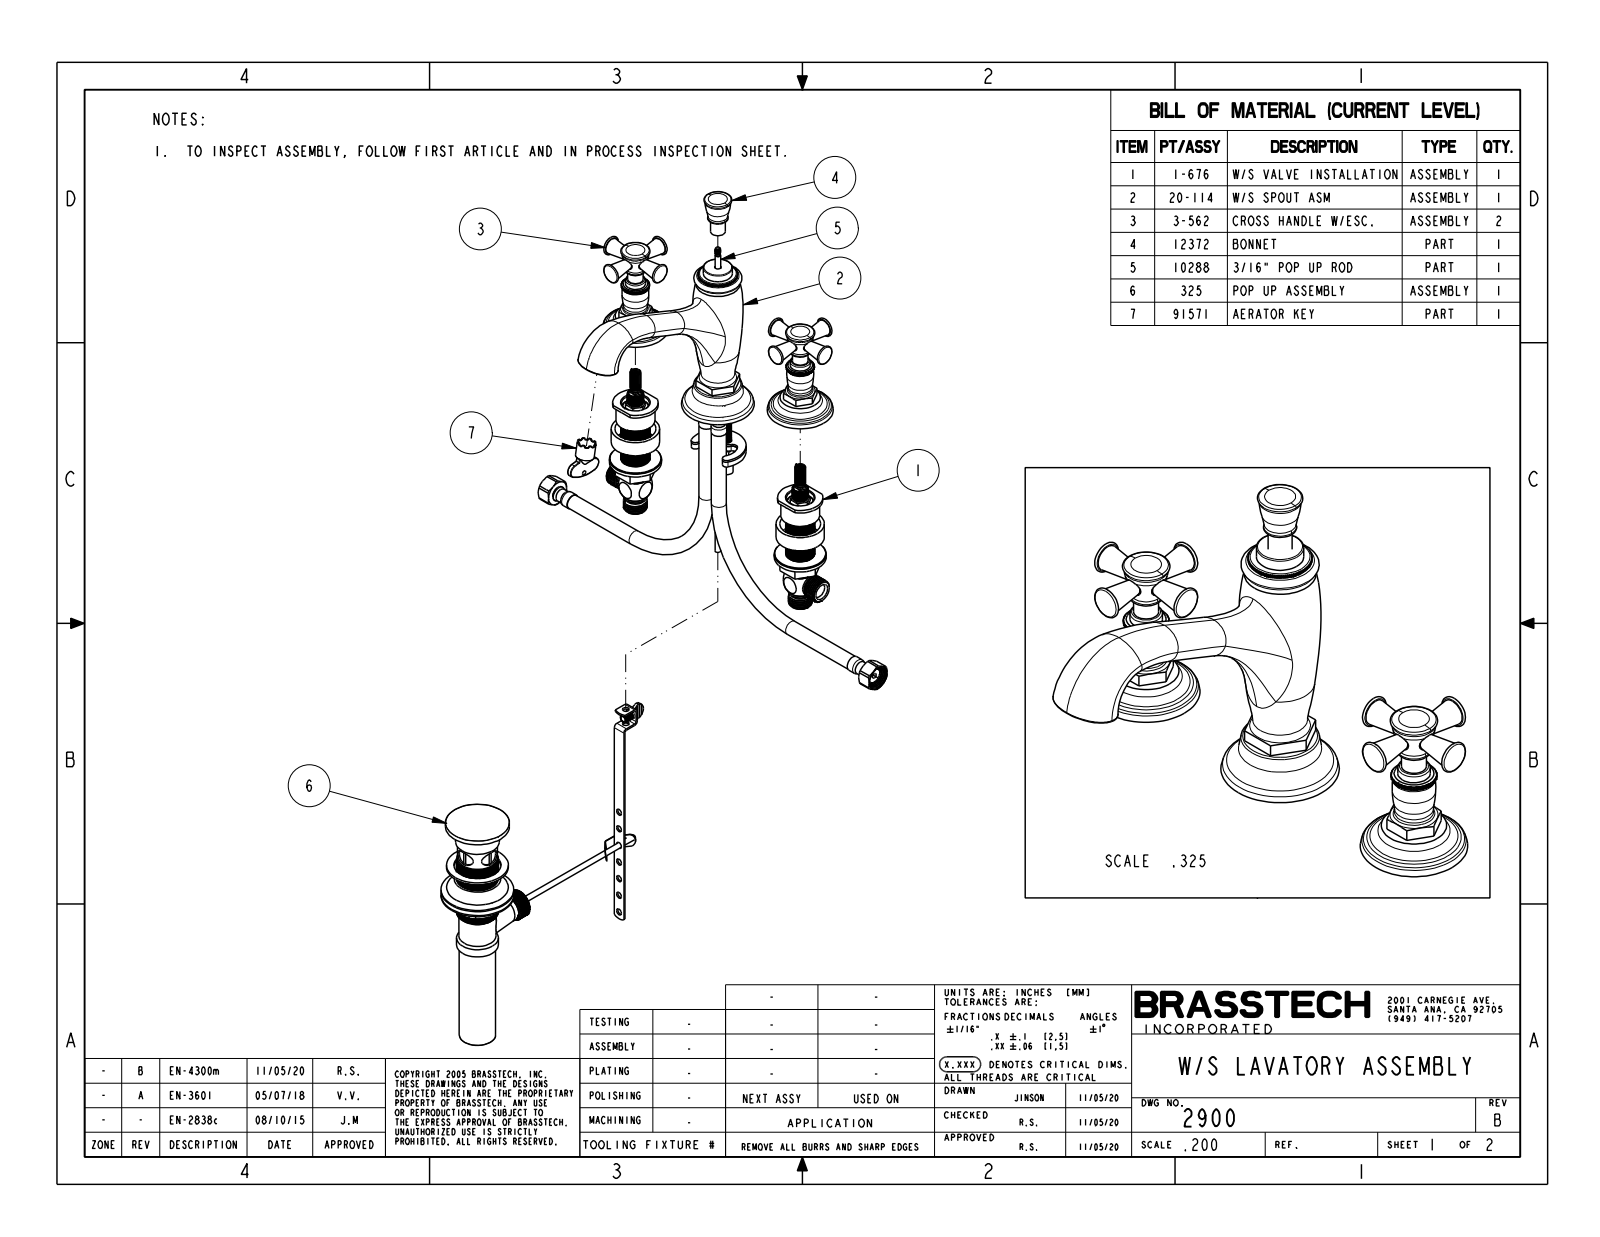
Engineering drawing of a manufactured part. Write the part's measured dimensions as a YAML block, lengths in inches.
part_name: "12370_1_1_1; 40553_1_1_1; 2900-_ASM"
step_written_by: "CREO PARAMETRIC BY PTC INC, 2018400 (CONFIG_CONTROL_DESIGN)"
units: inches
bodies: {solids: 3, faces: 1115, planar: 642, cylindrical: 40, other: 433}
overall_size: [10.45, 7.629, 7.144]
volume: 24.36
surface_area: 111.7
round_holes:
  - {diameter: 0.738, count: 1}
round_bosses_or_shafts:
  - {diameter: 0.98, count: 2}
  - {diameter: 0.686, count: 2}
  - {diameter: 0.53, count: 2}
  - {diameter: 1.12, count: 1}
  - {diameter: 1, count: 1}
  - {diameter: 0.75, count: 1}
  - {diameter: 0.51, count: 1}
partial_cylinders:
  - {radius: 0.28, count: 2}
face_to_face_distances: [0.534, 0.85, 0.316, 2.28, 3.623, 3.305, 4.648, 1.025, 6.928, 1.343]
